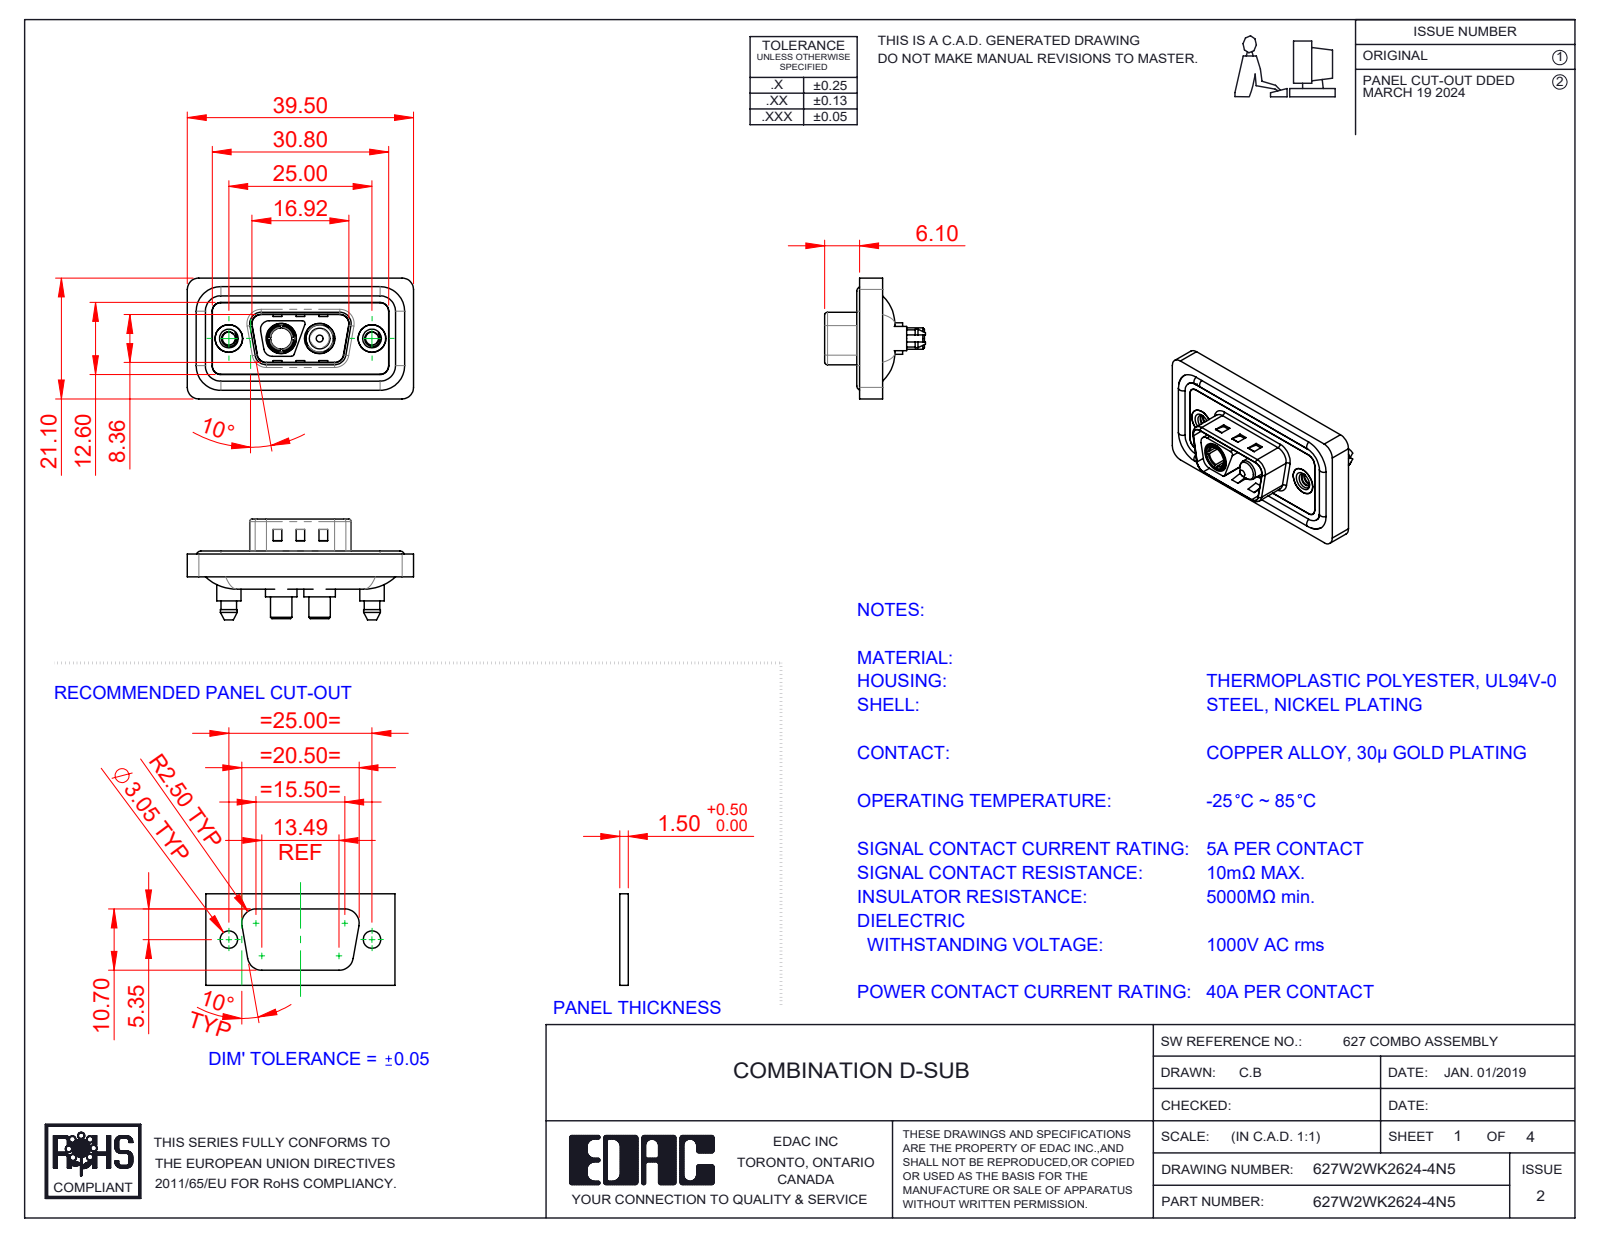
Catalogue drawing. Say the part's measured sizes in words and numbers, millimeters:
The part is named "Power Pin_40A S; 627Combo Shell Rear_09 Contacts; 627W2WK2624-4N5; 627Combo Waterproof Housing_09 Contacts (+4 more)". Its 3-D file was written by "SolidWorks 2023 (CONFIG_CONTROL_DESIGN)". It is 11 solids with 584 faces: 205 planar, 259 cylindrical and 120 other. Overall it measures 39.5 by 21.1 by 17.6 millimeters. Its volume is 4 725 cubic millimeters and its surface area 7 697 square millimeters. Round holes: 2 of diameter 2.26, 2 of diameter 4, 2 of diameter 4.8, 2 of diameter 4.85, 2 of diameter 5, 2 of diameter 5.3, 1 of diameter 3.7. Round bosses or shafts: 4 of diameter 1.6, 2 of diameter 5.5, 2 of diameter 5.4, 2 of diameter 5.2, 2 of diameter 4.9, 2 of diameter 4.75, 2 of diameter 4.25, 2 of diameter 3.75. Partial cylindrical surfaces (rounded edges, fillets, slot ends): 26 of radius 1.5, 18 of radius 2, 10 of radius 0.5, 10 of radius 1.6, 4 of radius 0.25, 4 of radius 0.6, 4 of radius 0.65, 4 of radius 0.9. The main face-to-face distances are 0.4, 1.1, 2.9, 3.1, 0.5, 1.6, 1.5, 4, 1.8, 3.2. The hole center spacings are 9.14, 15.86, 6.72, 25.
